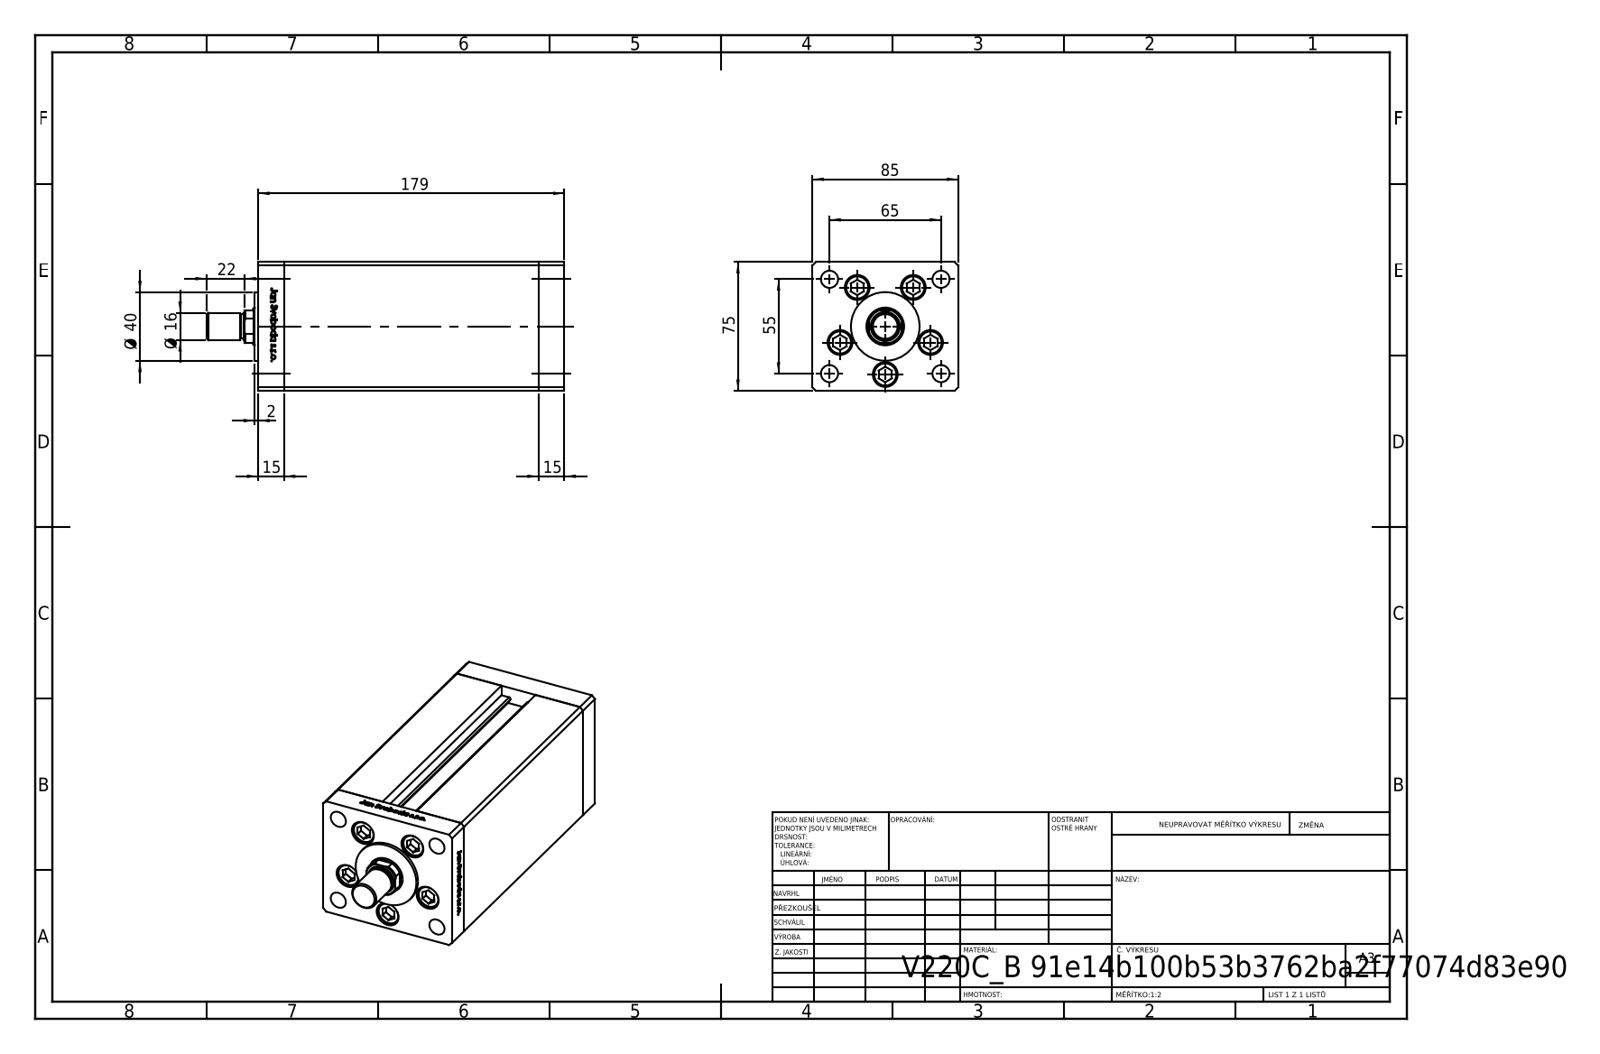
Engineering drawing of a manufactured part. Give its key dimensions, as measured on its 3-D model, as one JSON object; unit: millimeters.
{"part_name": "V220C_B MIDDLE; V220C_FRONT_B; V220C_B_VC; ALLEN BOLT (+2 more)", "step_written_by": "SolidWorks 2019 (CONFIG_CONTROL_DESIGN)", "units": "millimeters", "bodies": {"solids": 15, "faces": 1191, "planar": 466, "cylindrical": 147, "other": 578}, "overall_size": [208.5, 85, 75], "volume_mm3": 1014000, "surface_area_mm2": 159786, "round_holes": [[11, 5], [14.5, 5], [10, 4], [2, 2], [13.16, 2], [15, 1], [22, 1]], "round_bosses_or_shafts": [[8, 5], [40, 1], [16, 1], [14, 1]], "partial_cylinders_radius": [[0.93, 2], [10.5, 1]], "face_to_face_distances": [85, 75, 148.5, 15, 163.5, 178.5, 68.5, 9, 64.5, 10.5], "hole_center_spacings": [28, 42.57, 16.86, 19.17, 32.33, 32.5, 33.63, 37.33]}
